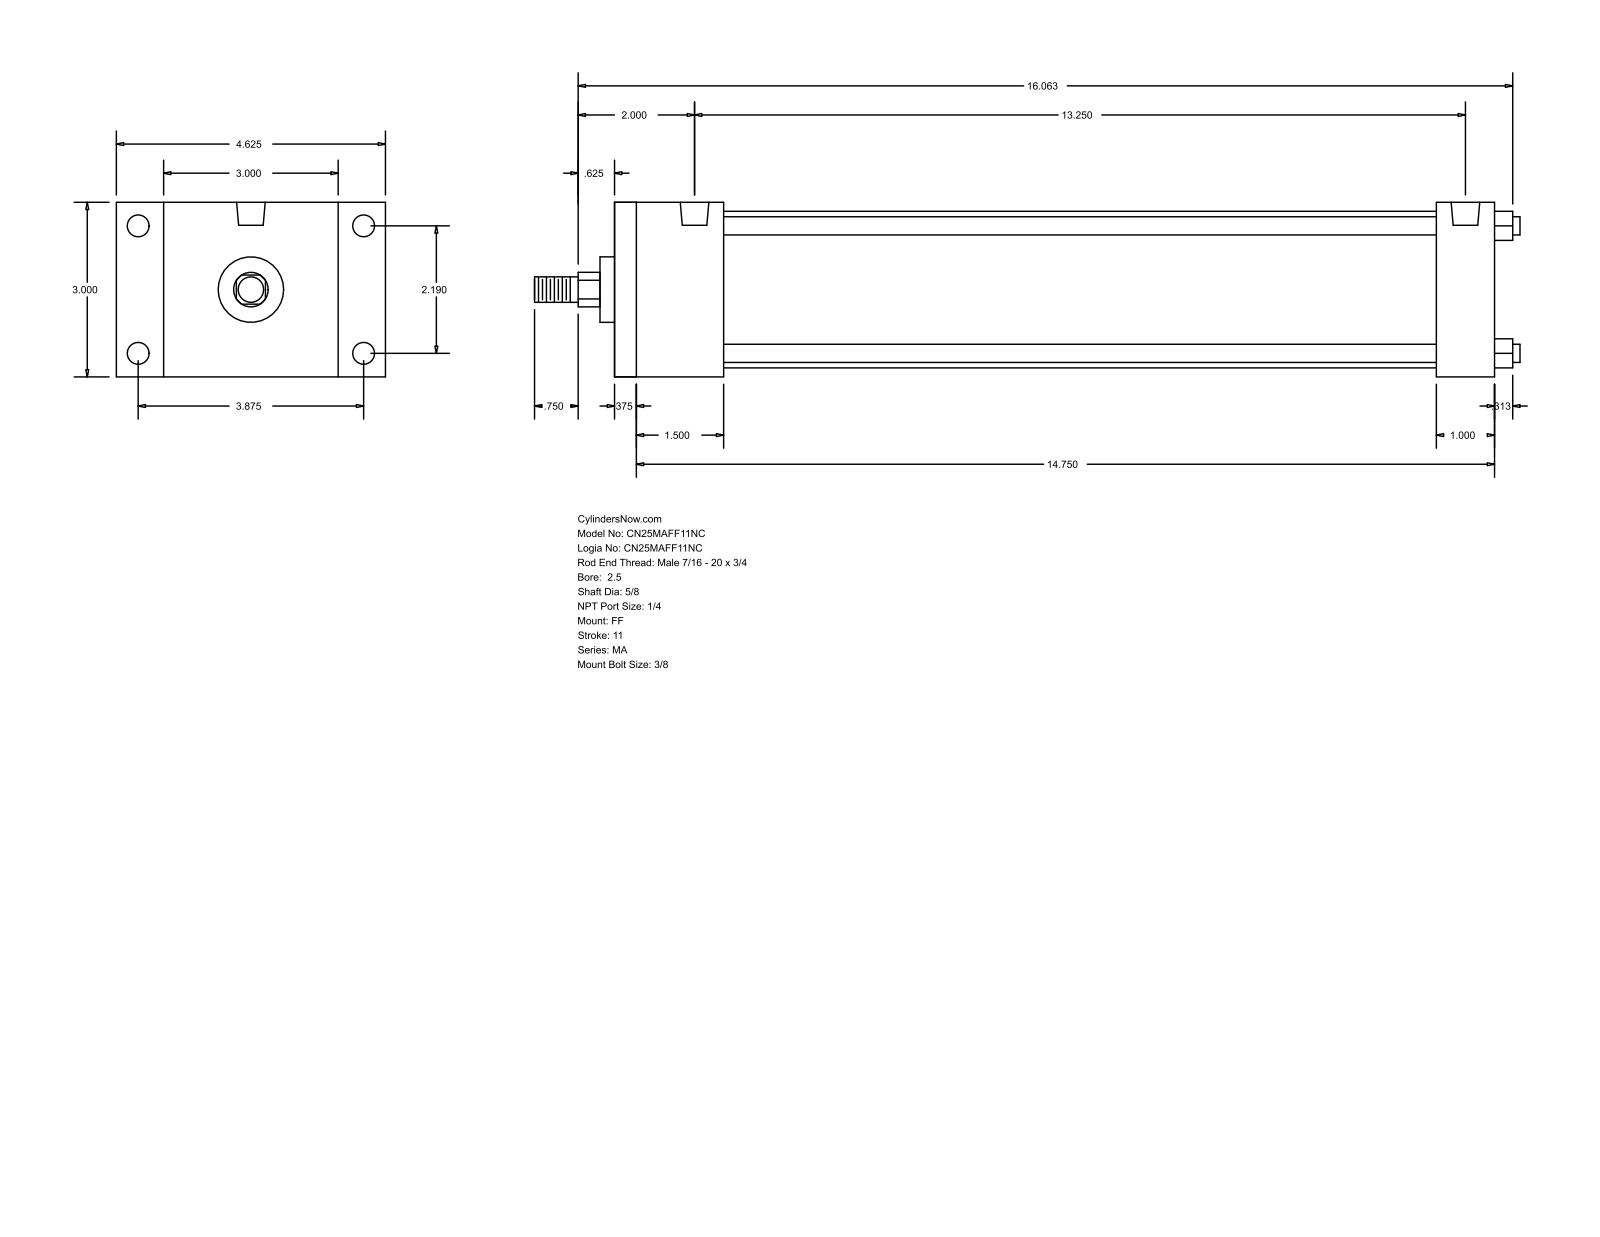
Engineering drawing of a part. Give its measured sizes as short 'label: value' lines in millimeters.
name: MA_FF__0250_0.625
written by: GSSL Pune (CONFIG_CONTROL_DESIGN)
unit: mm
bodies: 0 solids, 92 faces (64 planar, 28 cylindrical, 0 other)
size: 430.21 × 117.47 × 76.2
holes: 4× ⌀7.94, 4× ⌀9.53, 2× ⌀12.49
bosses: 4× ⌀7.94, 1× ⌀68.33, 1× ⌀28.57, 1× ⌀15.88, 1× ⌀11.11
rounds: 1× R7.54
face distances: 76.2, 384.17, 374.65, 9.52, 25.4, 47.62, 358.77, 38.1, 349.25, 311.15
hole spacings: 55.62, 98.42, 113.05, 336.55
